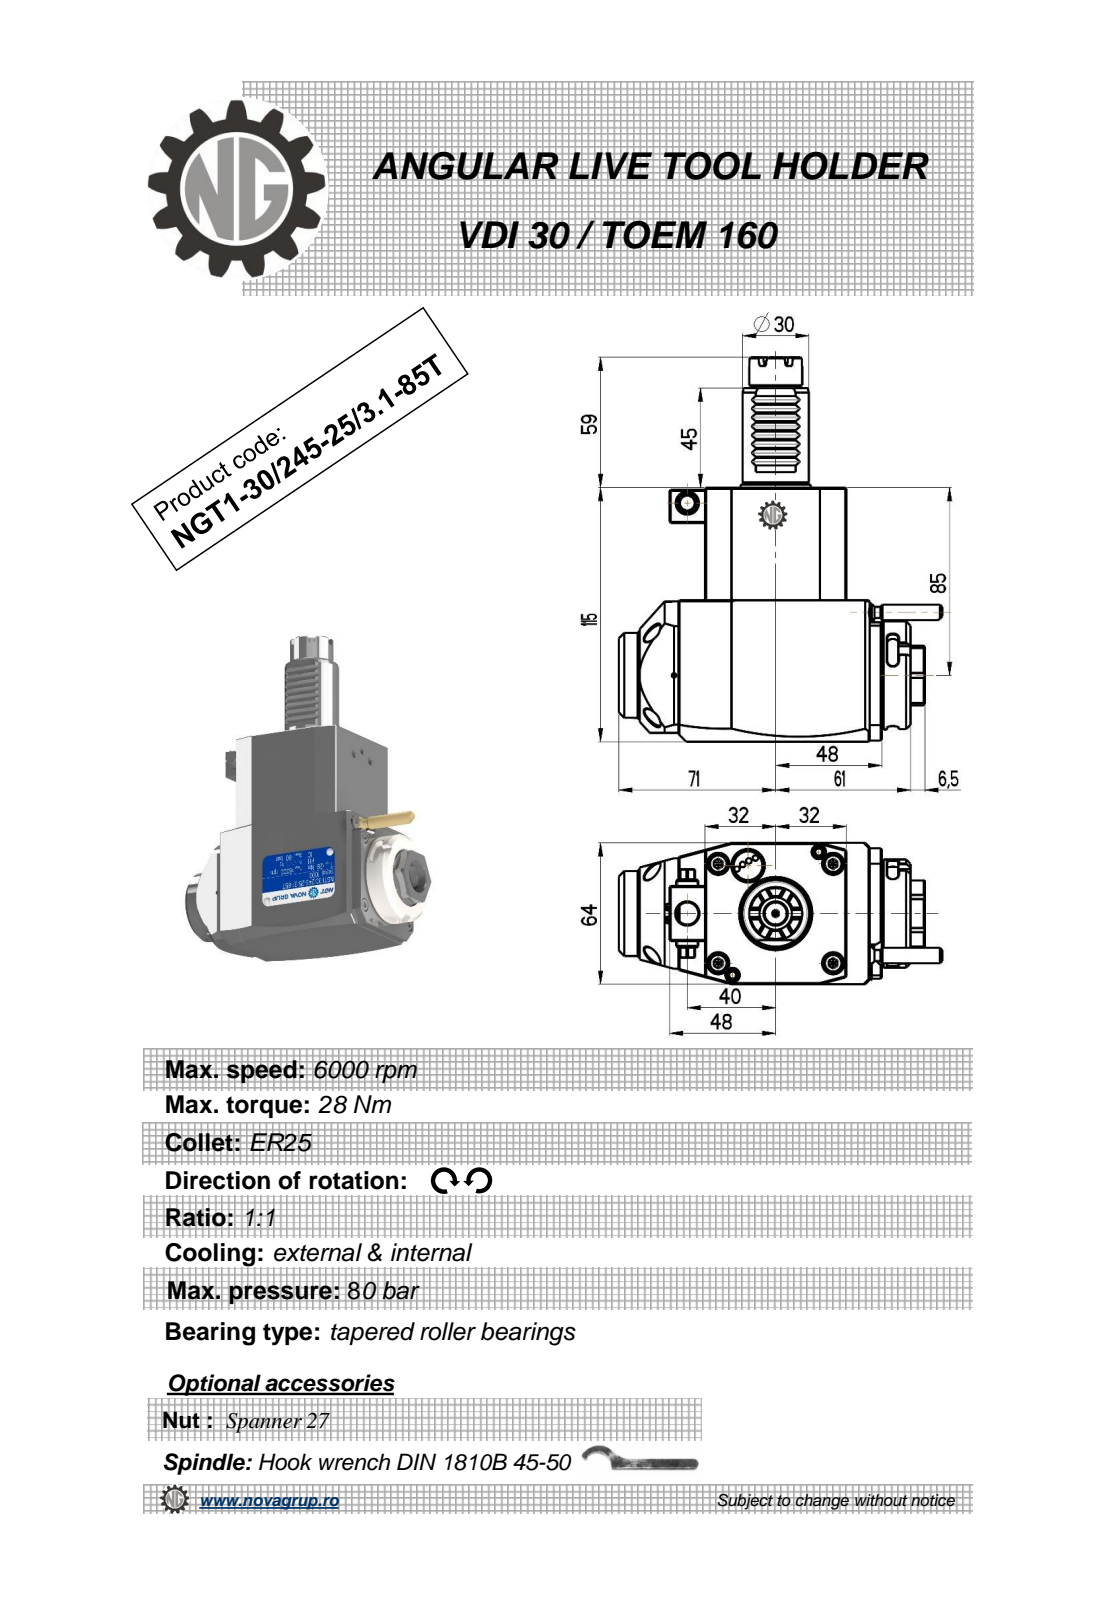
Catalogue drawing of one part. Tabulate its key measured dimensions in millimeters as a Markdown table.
| quantity | value |
| --- | --- |
| part name | NGT1_30_245_25_3_1_85T |
| STEP written by | PRO/ENGINEER BY PARAMETRIC TECHNOLOGY CORPORATION, 2010280 (CONFIG_CONTROL_DESIGN) |
| units | millimeters |
| bodies | 1 solid, 380 faces (212 planar, 84 cylindrical, 84 other) |
| overall size | 174 × 146.38 × 64 |
| volume | 683 916 mm³ |
| surface area | 58 453 mm² |
| round holes (diameter × count) | 2.5 × 1, 3 × 1, 8.5 × 1, 9.5 × 1, 10 × 1, 18 × 1 |
| round bosses / shafts (diameter × count) | 8 × 2, 49 × 1, 42 × 1, 38.5 × 1, 30 × 1, 24 × 1, 17.7 × 1, 15.2 × 1 |
| partial cylindrical surfaces (radius × count) | 0.3 × 8, 2.5 × 6, 180 × 2, 3.85 × 1, 4.5 × 1, 15 × 1, 21.5 × 1, 33.5 × 1 |
| main face-to-face distances | 64, 115, 16, 80, 13, 51, 72.18, 93, 29, 39 |
| hole center spacings | 34.25, 51.62, 76.5 |
